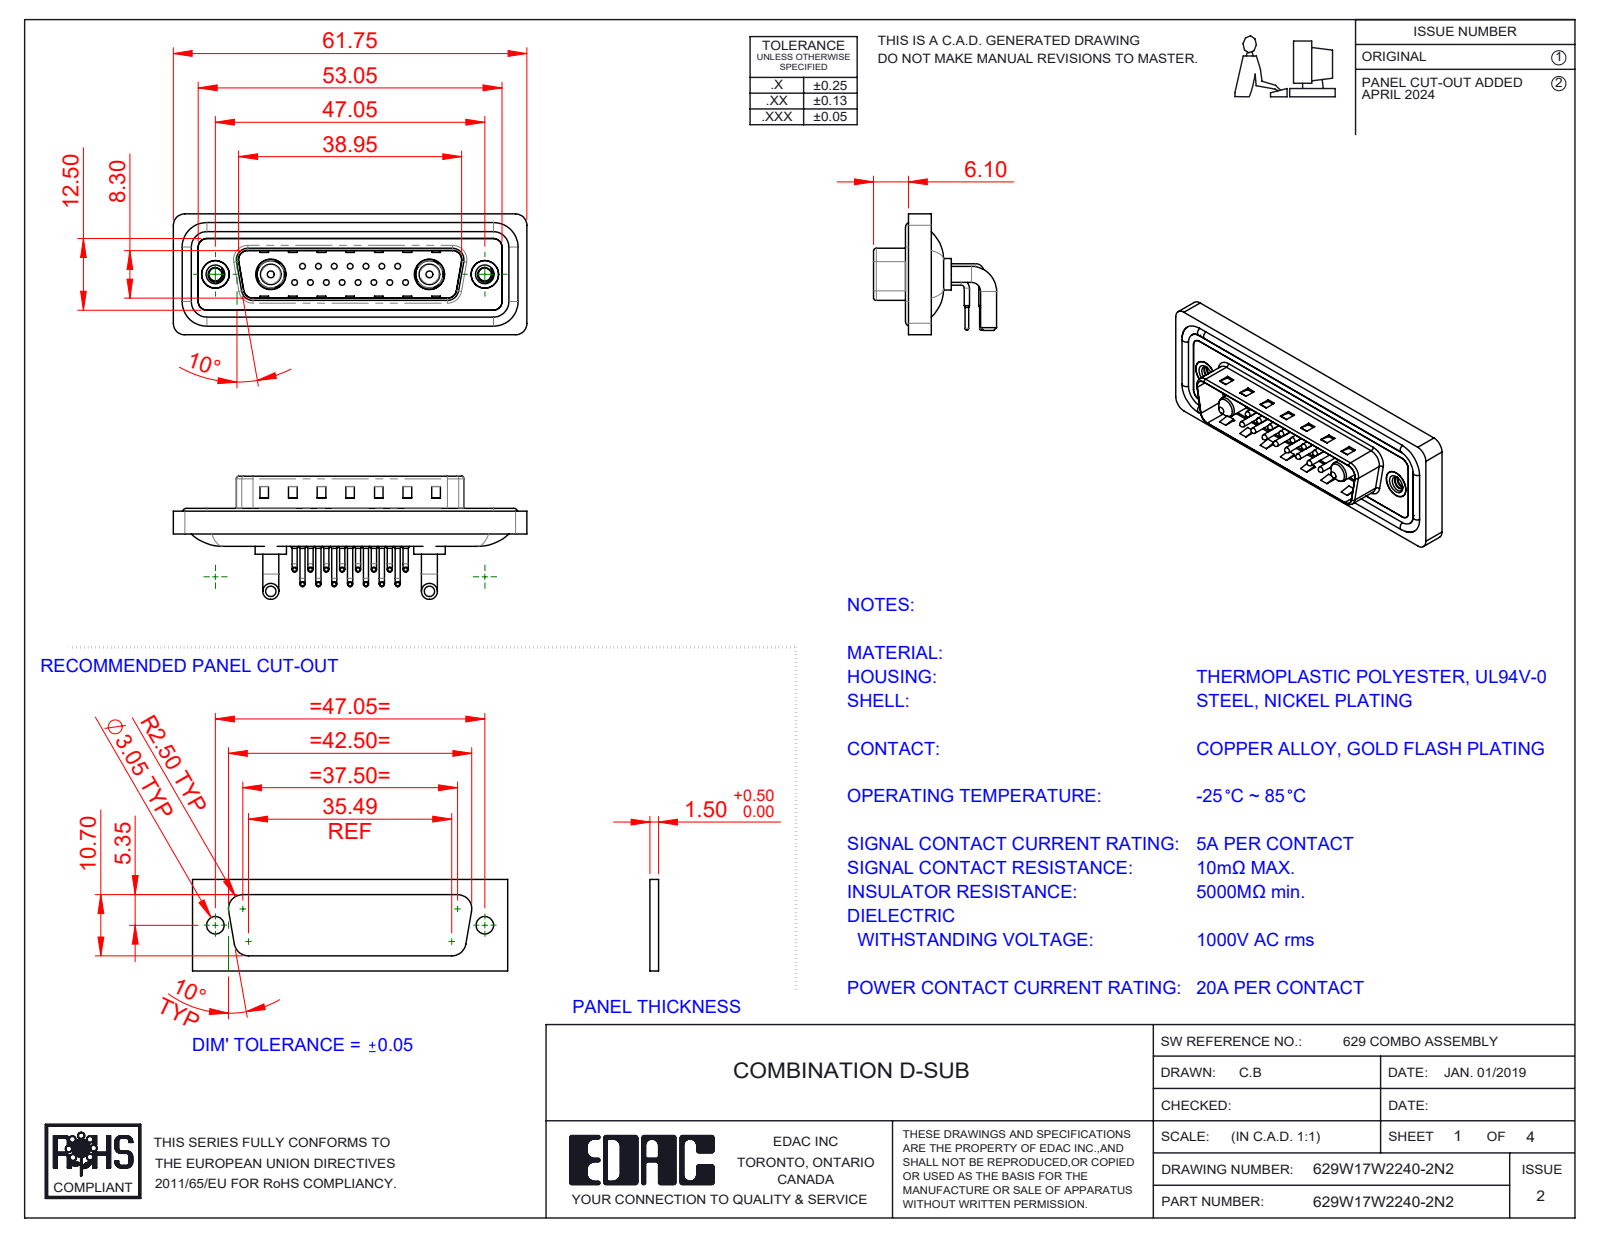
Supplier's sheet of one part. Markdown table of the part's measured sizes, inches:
| quantity | value |
| --- | --- |
| part name | 629Combo Contact Row 2; 629Combo Contact Row 1; 629Combo Waterproof Housing_25 Contacts; 629Combo Shell Rear_25 Contacts (+5 more) |
| STEP written by | SolidWorks 2023 (CONFIG_CONTROL_DESIGN) |
| units | inches |
| bodies | 26 solids, 2219 faces (1189 planar, 770 cylindrical, 260 other) |
| overall size | 2.431 × 0.846 × 0.831 |
| volume | 0.459 in³ |
| surface area | 19.53 in² |
| round holes (diameter × count) | 0.03 × 15, 0.063 × 15, 0.079 × 15, 0.089 × 2, 0.157 × 2, 0.189 × 2, 0.191 × 2, 0.197 × 2, 0.209 × 2 |
| round bosses / shafts (diameter × count) | 0.035 × 30, 0.059 × 15, 0.039 × 15, 0.026 × 15, 0.11 × 4, 0.063 × 4, 0.217 × 2, 0.205 × 2 |
| partial cylindrical surfaces (radius × count) | 0.059 × 18, 0.079 × 18, 0.04 × 15, 0.02 × 8, 0.063 × 8, 0.01 × 4, 0.024 × 4, 0.026 × 4 |
| main face-to-face distances | 0.016, 0.114, 0.031, 0.161, 0.043, 0.083, 0.063, 0.177, 0.059, 0.098 |
| hole center spacings | 0.124, 0.109, 0.218, 0.327, 0.198, 0.295, 0.436, 0.198 |
